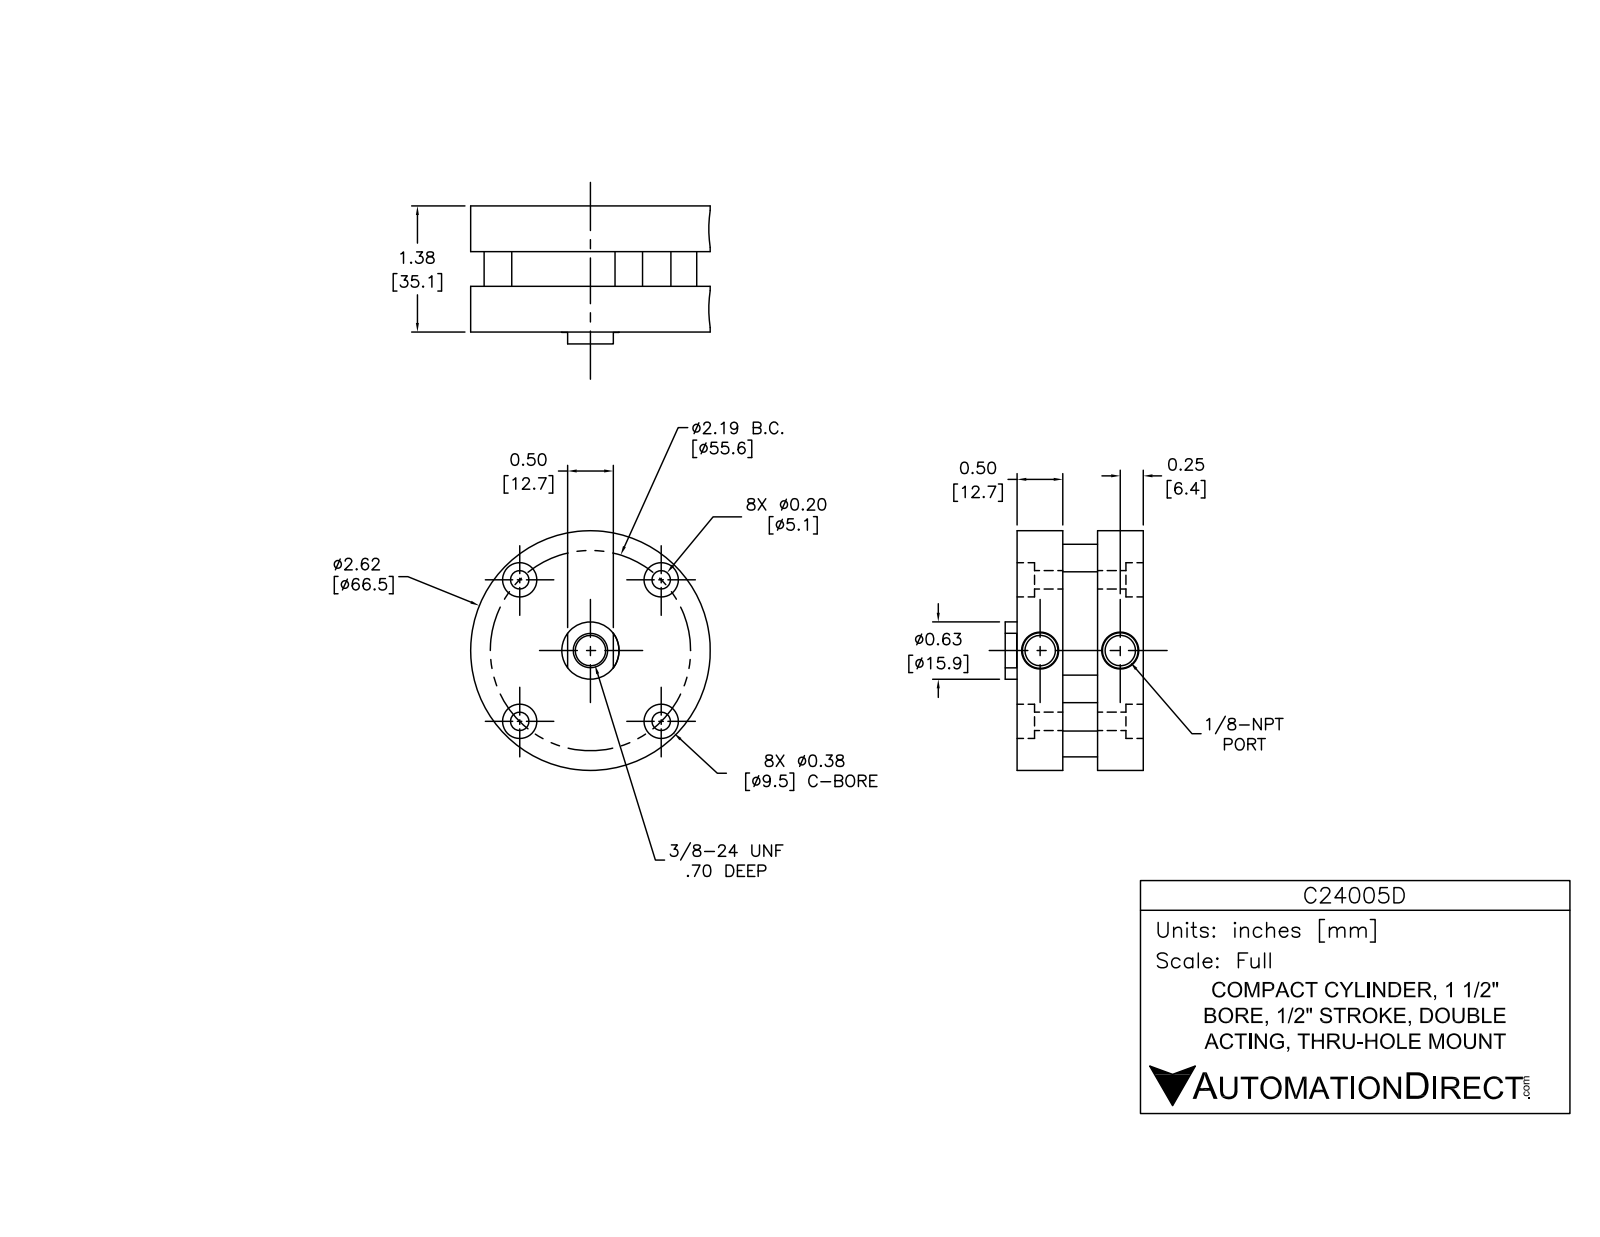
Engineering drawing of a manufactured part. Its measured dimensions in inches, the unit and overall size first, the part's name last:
Units: inches
Overall size (bounding box): 2.62 × 2.62 × 1.51
Round holes (diameter × count): ⌀0.2 ×4, ⌀0.218 ×4, ⌀0.343 ×4, ⌀0.125 ×2, ⌀0.33 ×1, ⌀0.63 ×1, ⌀0.632 ×1, ⌀1.503 ×1, ⌀1.563 ×1
Round bosses / shafts (diameter × count): ⌀0.4 ×4, ⌀2.62 ×1
Main face-to-face distances: 0.5, 0.282, 0.88, 0.598, 1.098, 0.218, 1.38, 0.38, 0.816, 0.316
Hole centre spacings: 1.095, 1.549, 0.428, 1.217, 1.821, 2.148, 2.19, 2.191
Volume: 5.234 in³ · Surface area: 57.57 in²
Bodies: 9 solids, 165 faces (49 planar, 98 cylindrical, 18 other)
Part name (STEP PRODUCT): C24005D; C24005D-rod_part; C24005D-FO1_BM_rod; C24005D-FO1_BM_heads (2) (+3 more)
STEP written by: SolidWorks 2014 (AUTOMOTIVE_DESIGN)
